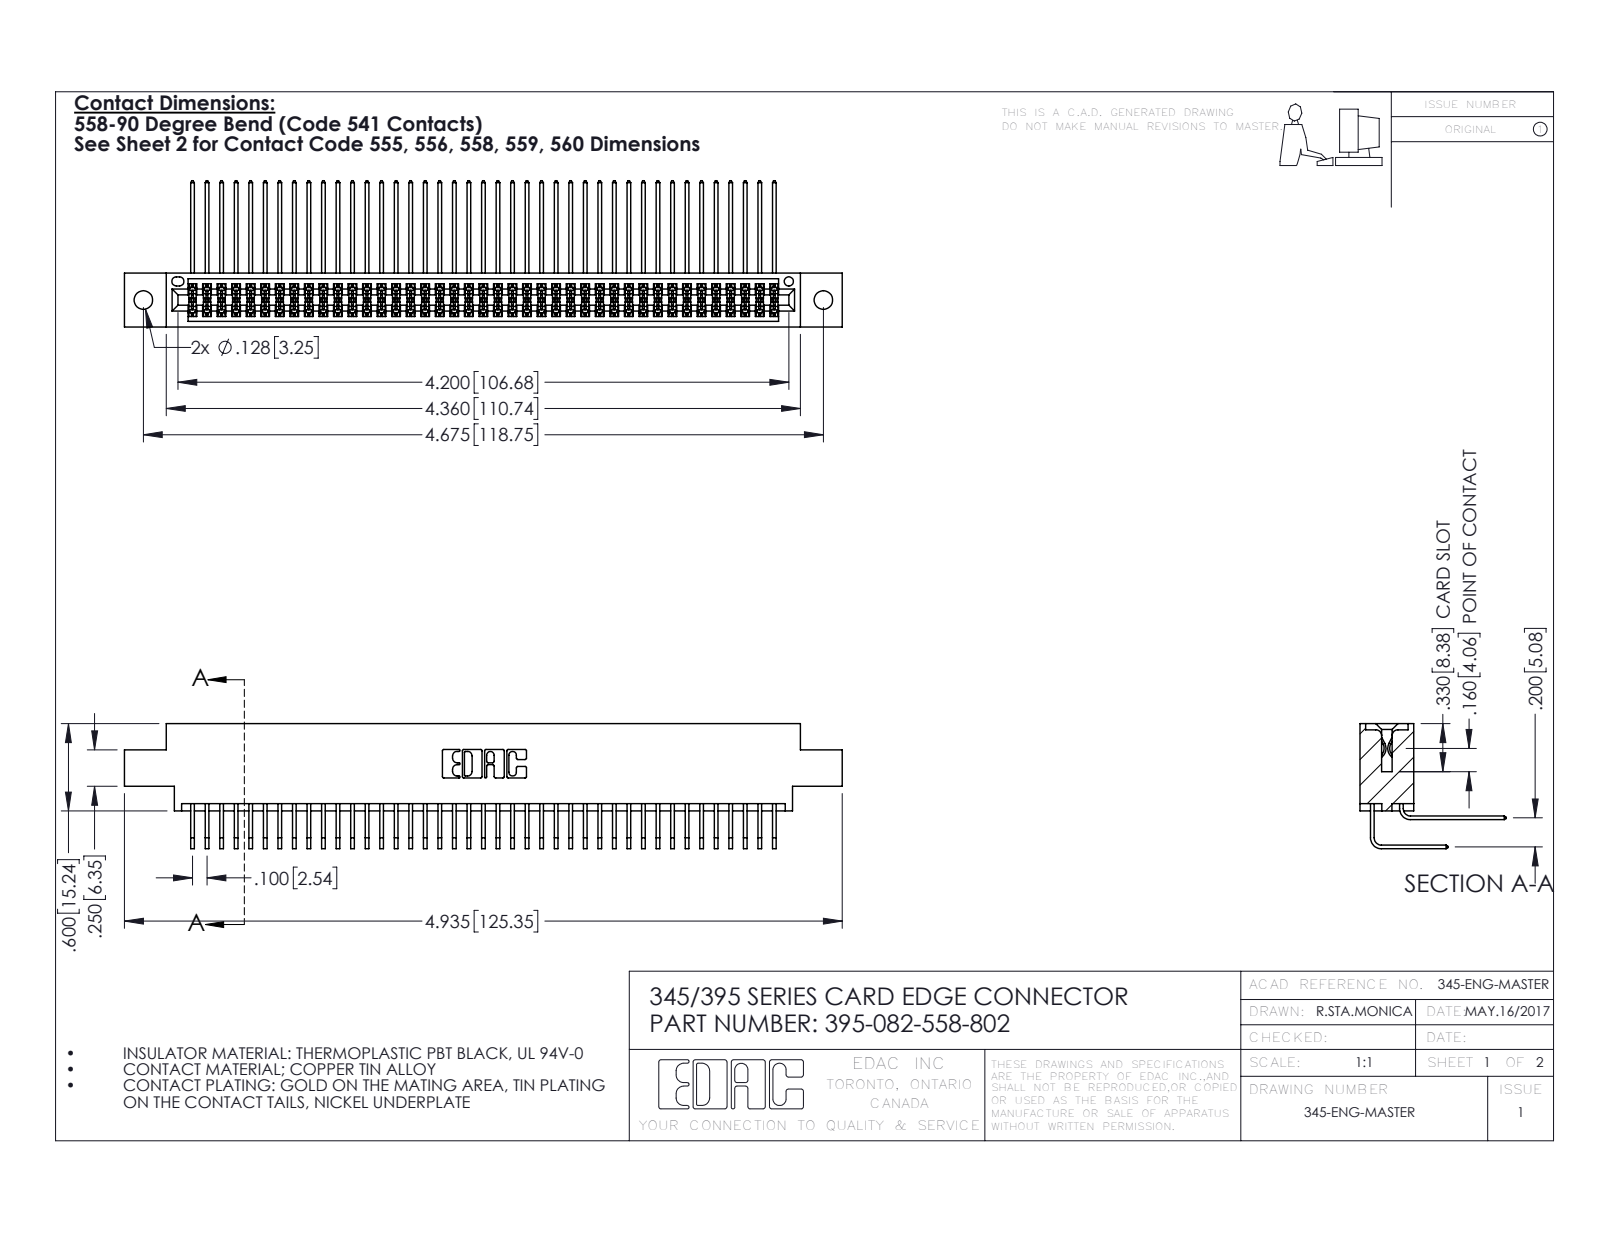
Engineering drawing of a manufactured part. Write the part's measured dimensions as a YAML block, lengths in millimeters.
part_name: "395-082-558-802; 345-292-001_558 559 Tail - 1; 345 Part_0.170 Offset - 0.128 Dia; 345-292-001_558 Tail - 2"
step_written_by: "SolidWorks 2016 (CONFIG_CONTROL_DESIGN)"
units: millimeters
bodies: {solids: 83, faces: 4394, planar: 2954, cylindrical: 1440, other: 0}
overall_size: [125.3, 25.5, 21.8]
volume: 12500
surface_area: 20540
round_holes:
  - {diameter: 3.3, count: 2}
  - {diameter: 1.6, count: 1}
partial_cylinders:
  - {radius: 0.2, count: 124}
  - {radius: 0.3, count: 22}
  - {radius: 0.2, count: 6}
  - {radius: 0.8, count: 6}
  - {radius: 0.7, count: 3}
  - {radius: 0.4, count: 2}
  - {radius: 0.5, count: 2}
  - {radius: 0.6, count: 2}
face_to_face_distances: [1.8, 7.6, 5.1, 9.4, 2.5, 6.9, 0.6, 5.7, 4.4, 0.6]
hole_center_spacings: [6.9, 112.8, 118.7]
